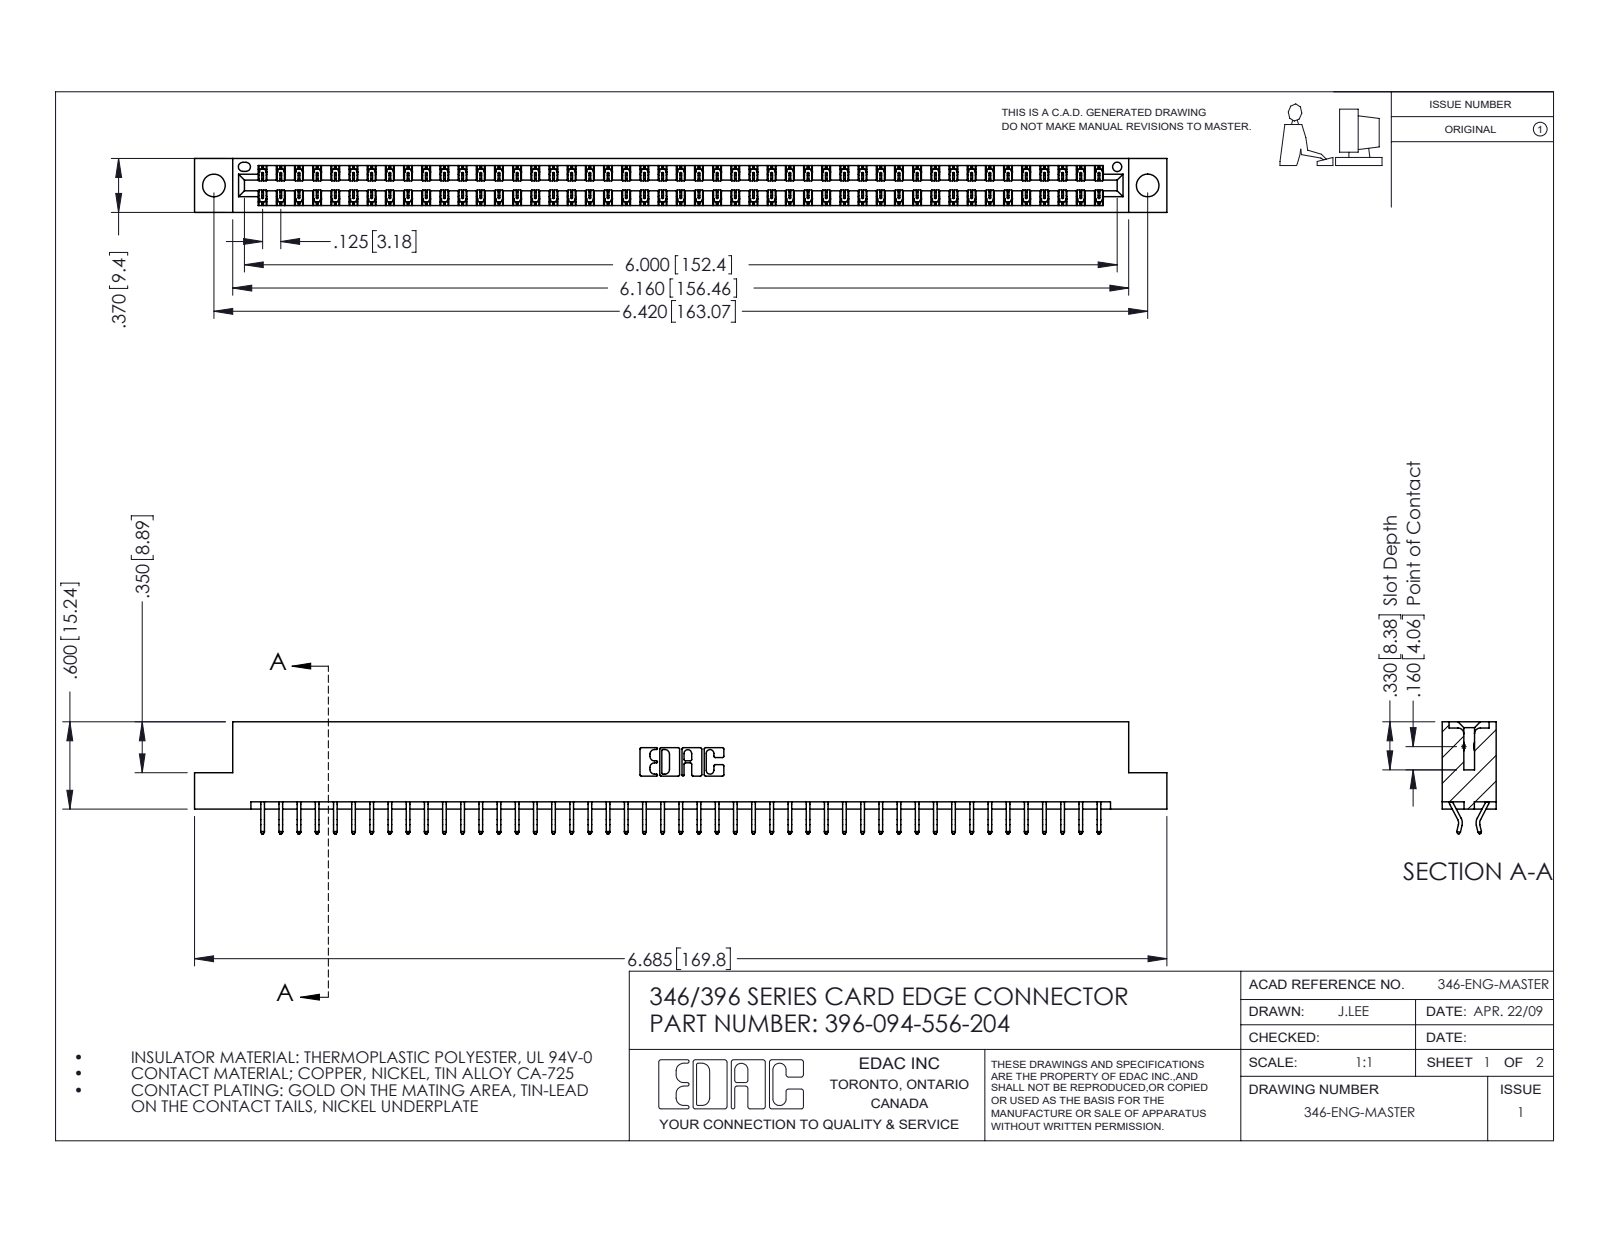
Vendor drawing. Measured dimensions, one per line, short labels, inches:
name: 345-292-001_556 Tail; 346 Part_Flush Mounting Lugs - 0.156 Dia-TH; 396-094-556-204
written by: SolidWorks 2016 (CONFIG_CONTROL_DESIGN)
unit: in
bodies: 95 solids, 5574 faces (3742 planar, 1832 cylindrical, 0 other)
size: 6.685 × 0.77 × 0.37
volume: 1.007 in³; area: 34.86 in²
holes: 2× ⌀0.156, 1× ⌀0.064
rounds: 141× R0.006, 22× R0.01, 6× R0.007, 6× R0.031, 3× R0.026, 2× R0.01, 2× R0.014, 2× R0.022
face distances: 0.048, 0.322, 0.37, 0.25, 0.025, 0.072, 0.298, 0.275, 0.148, 0.222
hole spacings: 0.246, 6.211, 6.42
